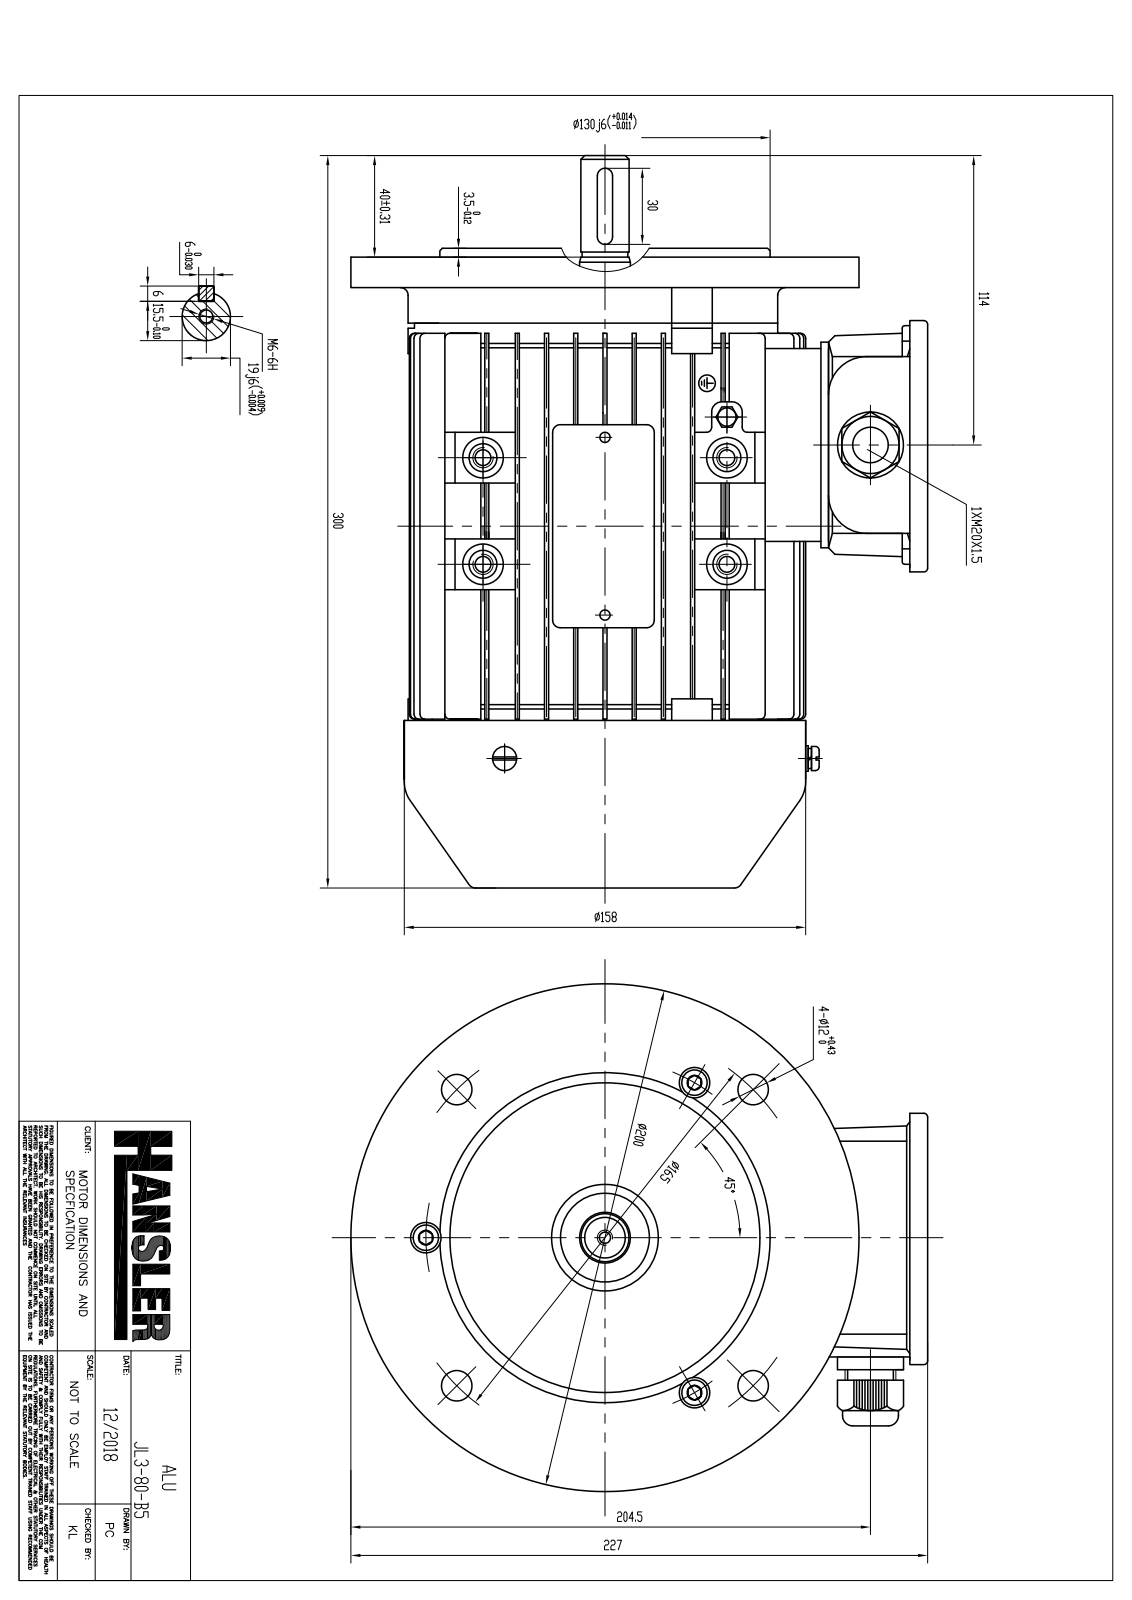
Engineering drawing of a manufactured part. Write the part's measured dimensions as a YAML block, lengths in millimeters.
part_name: "JL3-80-B5"
step_written_by: "DATAKIT 2018 (c) (AP242_MANAGED_MODEL_BASED_3D_ENGINEERING_MIM_LF)"
units: millimeters
bodies: {solids: 39, faces: 2166, planar: 1028, cylindrical: 634, other: 504}
overall_size: [357.89, 230.72, 200]
volume: 1241000
surface_area: 678525
round_holes:
  - {diameter: 4, count: 13}
  - {diameter: 16, count: 10}
  - {diameter: 6.6, count: 8}
  - {diameter: 12, count: 7}
  - {diameter: 5.25, count: 4}
  - {diameter: 5.3, count: 4}
  - {diameter: 5.8, count: 4}
  - {diameter: 7, count: 4}
  - {diameter: 6.39, count: 3}
  - {diameter: 2, count: 2}
  - {diameter: 9.6, count: 2}
  - {diameter: 11.46, count: 2}
round_bosses_or_shafts:
  - {diameter: 11, count: 8}
  - {diameter: 10, count: 7}
  - {diameter: 12, count: 4}
  - {diameter: 7.85, count: 4}
  - {diameter: 7, count: 4}
  - {diameter: 6, count: 4}
  - {diameter: 5, count: 4}
  - {diameter: 4.48, count: 4}
partial_cylinders:
  - {radius: 2, count: 73}
  - {radius: 3, count: 31}
  - {radius: 4, count: 26}
  - {radius: 0.33, count: 20}
  - {radius: 0.3, count: 16}
  - {radius: 0.39, count: 12}
  - {radius: 1.97, count: 12}
  - {radius: 5, count: 12}
face_to_face_distances: [1.6, 11.5, 23, 34.5, 10.57, 46, 9.9, 13.1, 21.14, 21.4]
hole_center_spacings: [70.5, 122.11, 14.14, 42, 54, 82.5, 82.51, 87]
